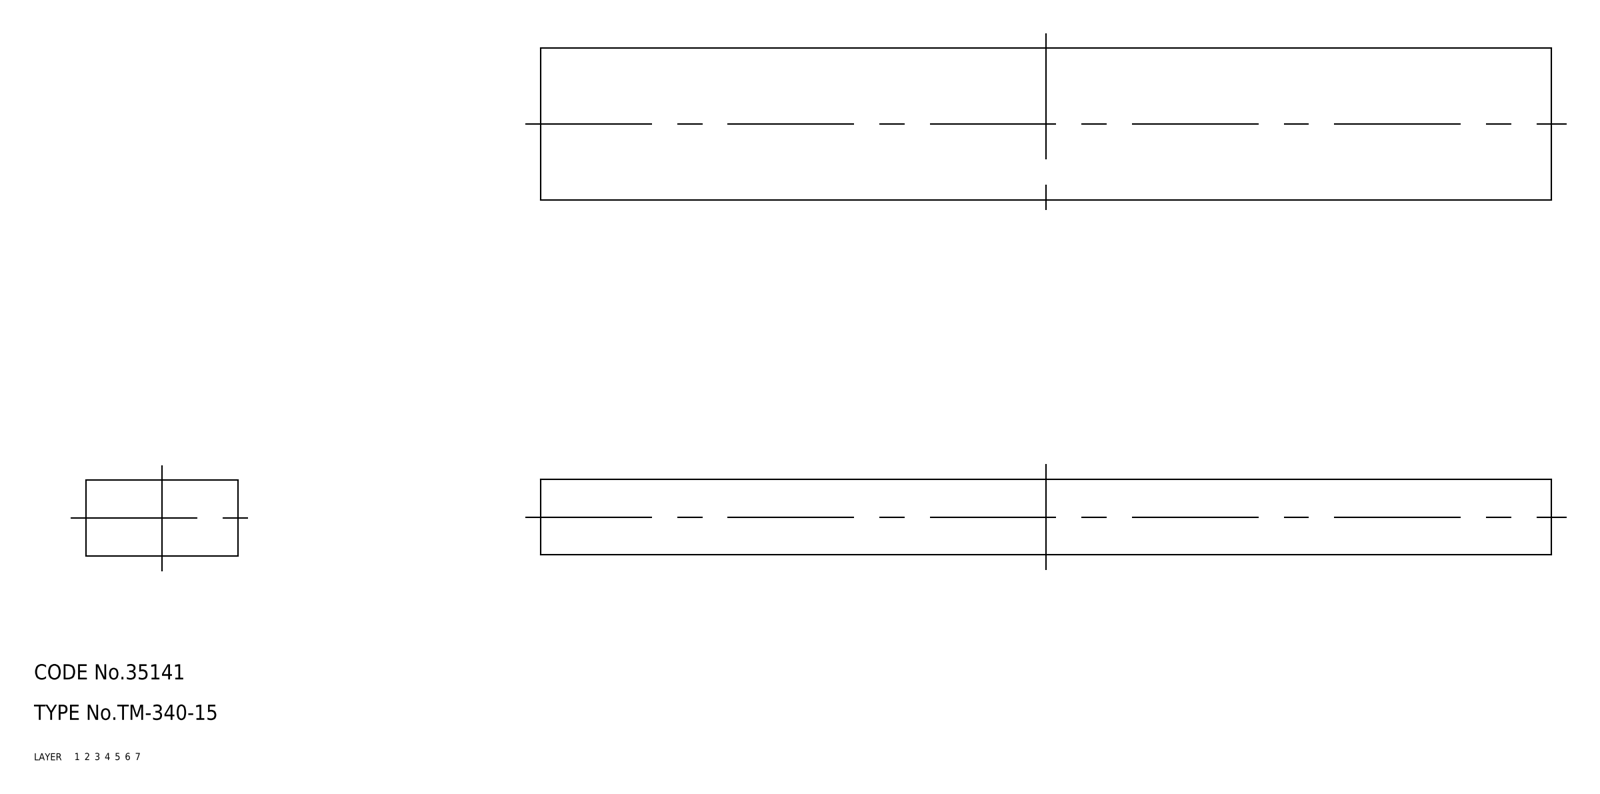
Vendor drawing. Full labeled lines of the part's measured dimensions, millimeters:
Part name (STEP PRODUCT): TM_340_15; rubber foam
STEP written by: SolidWorks 2015 (AUTOMOTIVE_DESIGN)
Units: millimetres
Bodies: 1 solid, 6 faces (6 planar, 0 cylindrical, 0 other)
Overall size (bounding box): 200 × 30 × 15
Volume: 90 000 mm³ · Surface area: 18 900 mm²
Main face-to-face distances: 15, 30, 200
